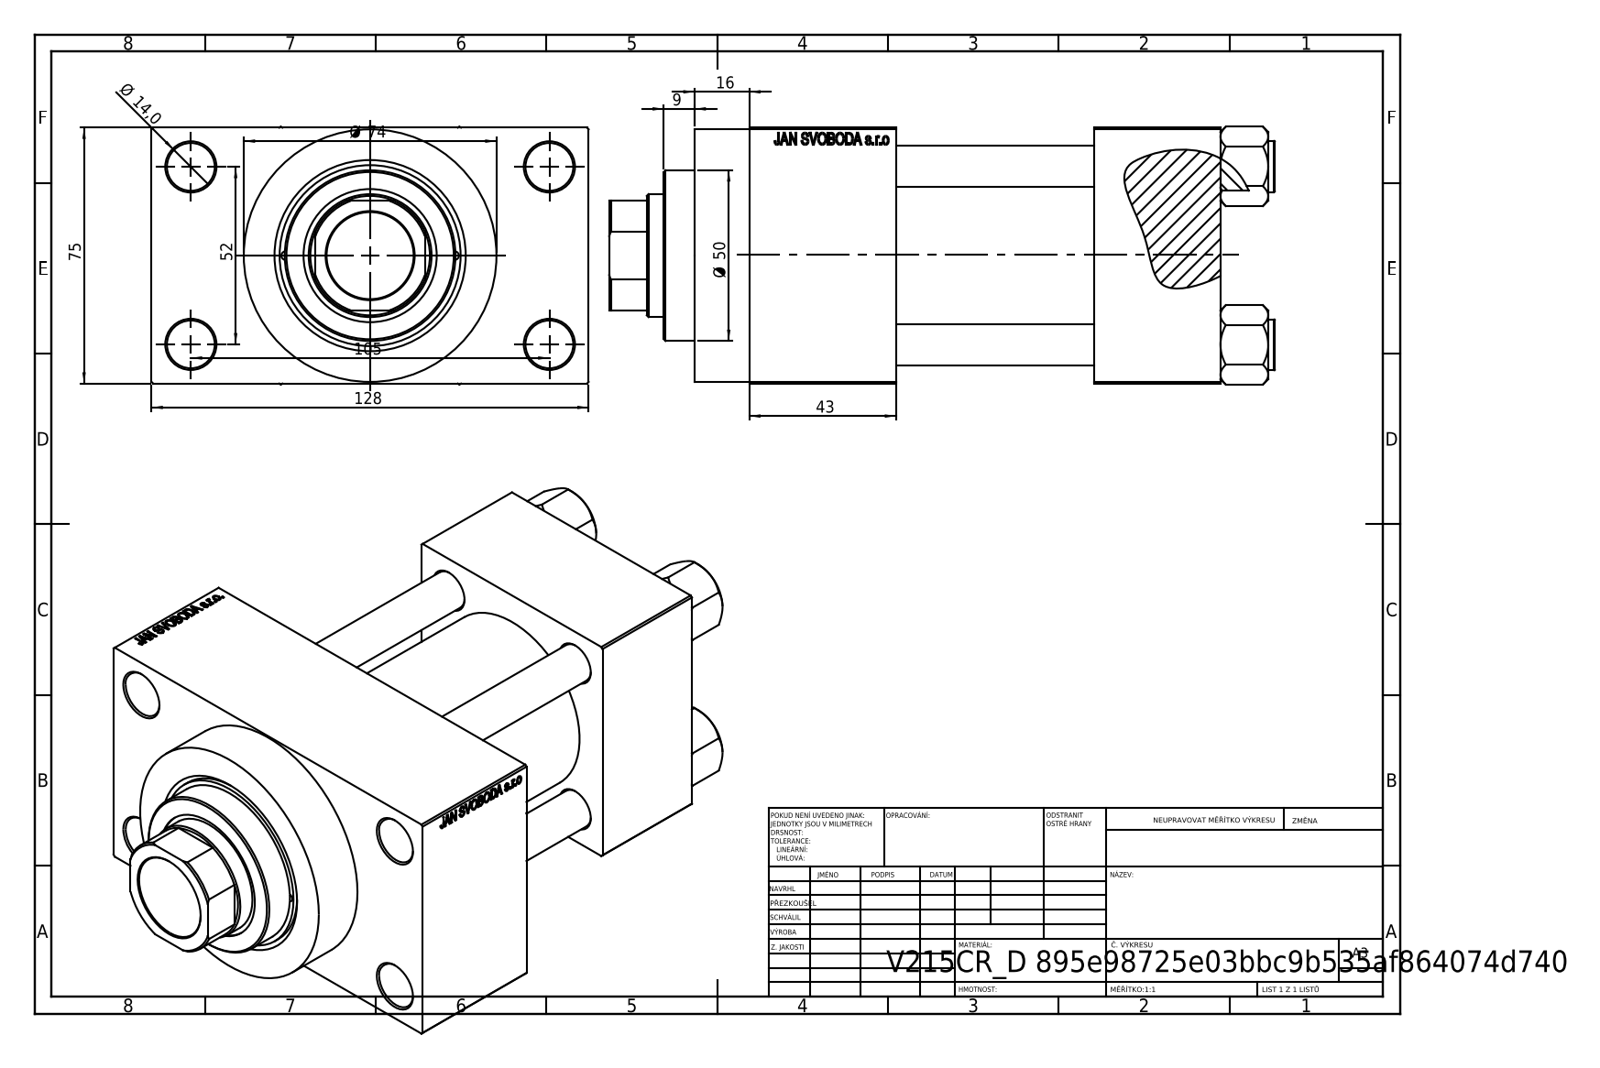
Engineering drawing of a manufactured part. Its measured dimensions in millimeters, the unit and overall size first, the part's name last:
Units: millimetres
Overall size (bounding box): 195 × 128 × 75.54
Round holes (diameter × count): ⌀12 ×4, ⌀14 ×4, ⌀2.5 ×2, ⌀7 ×2, ⌀20.96 ×2, ⌀30 ×2, ⌀25.5 ×1, ⌀36 ×1, ⌀39 ×1, ⌀41 ×1, ⌀53 ×1
Round bosses / shafts (diameter × count): ⌀15 ×4, ⌀74 ×1, ⌀56 ×1, ⌀50 ×1
Partial cylindrical surfaces — rounded edges, fillets, slot ends (radius × count): R17.5 ×1
Main face-to-face distances: 75, 58, 37, 95, 26.5, 43, 138, 101, 101.5, 16
Hole centre spacings: 26.19, 26.35, 36.98, 38.03, 52.3, 57.22, 58.43, 58.59
Volume: 817 073 mm³ · Surface area: 175 479 mm²
Bodies: 11 solids, 1113 faces (501 planar, 92 cylindrical, 520 other)
Part name (STEP PRODUCT): V215CR_VCP_D; V215CR_D_TYCINKA; V215_VC_A; NUT_M5_D (+1 more)
STEP written by: SolidWorks 2019 (CONFIG_CONTROL_DESIGN)
